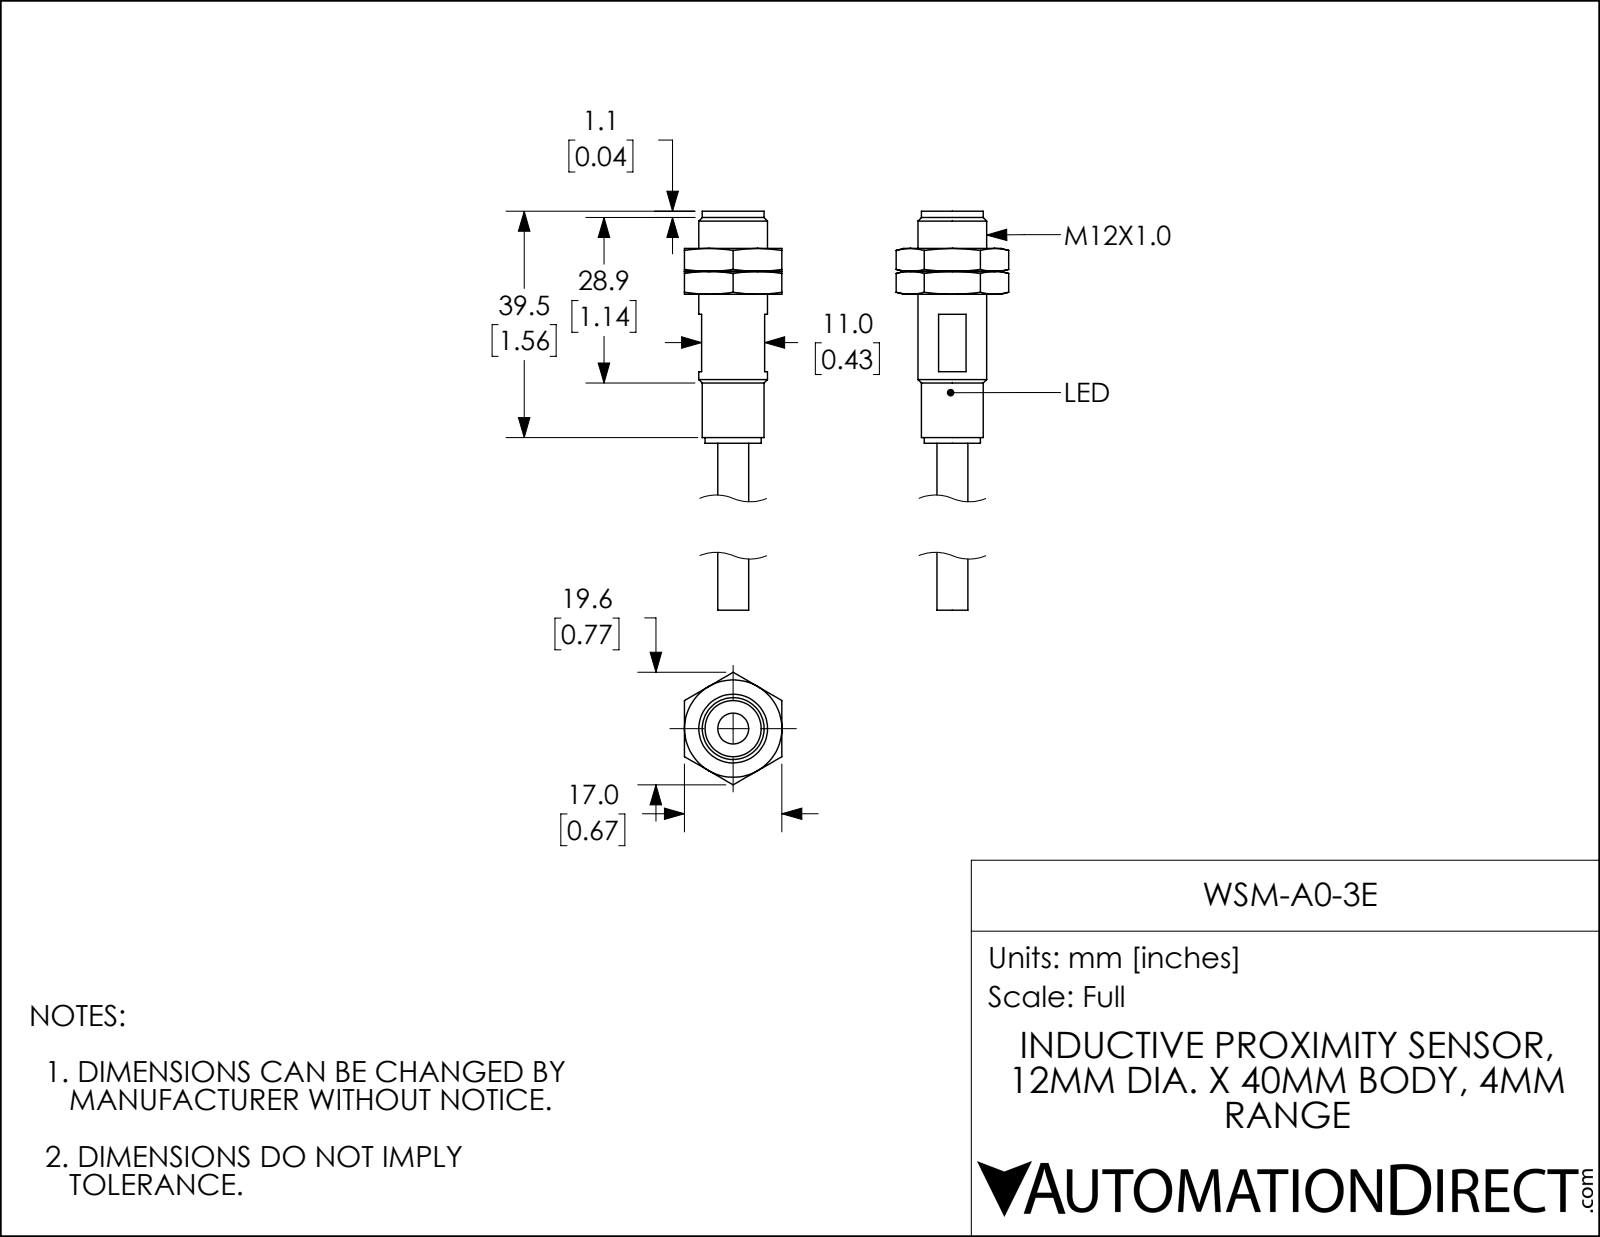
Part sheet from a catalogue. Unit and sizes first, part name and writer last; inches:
Units: inches
Overall size (bounding box): 2.854 × 0.773 × 0.669
Round holes (diameter × count): ⌀0.43 ×1
Round bosses / shafts (diameter × count): ⌀0.472 ×1, ⌀0.425 ×1, ⌀0.386 ×1, ⌀0.213 ×1
Main face-to-face distances: 0.157, 0.669, 0.315, 0.118, 0.551, 0.413, 0.571, 0.256, 1.181, 1.024
Volume: 0.38 in³ · Surface area: 5.474 in²
Bodies: 3 solids, 65 faces (28 planar, 7 cylindrical, 30 other)
Part name (STEP PRODUCT): WSM-A0-3E
STEP written by: SolidWorks 2017 (AUTOMOTIVE_DESIGN)
